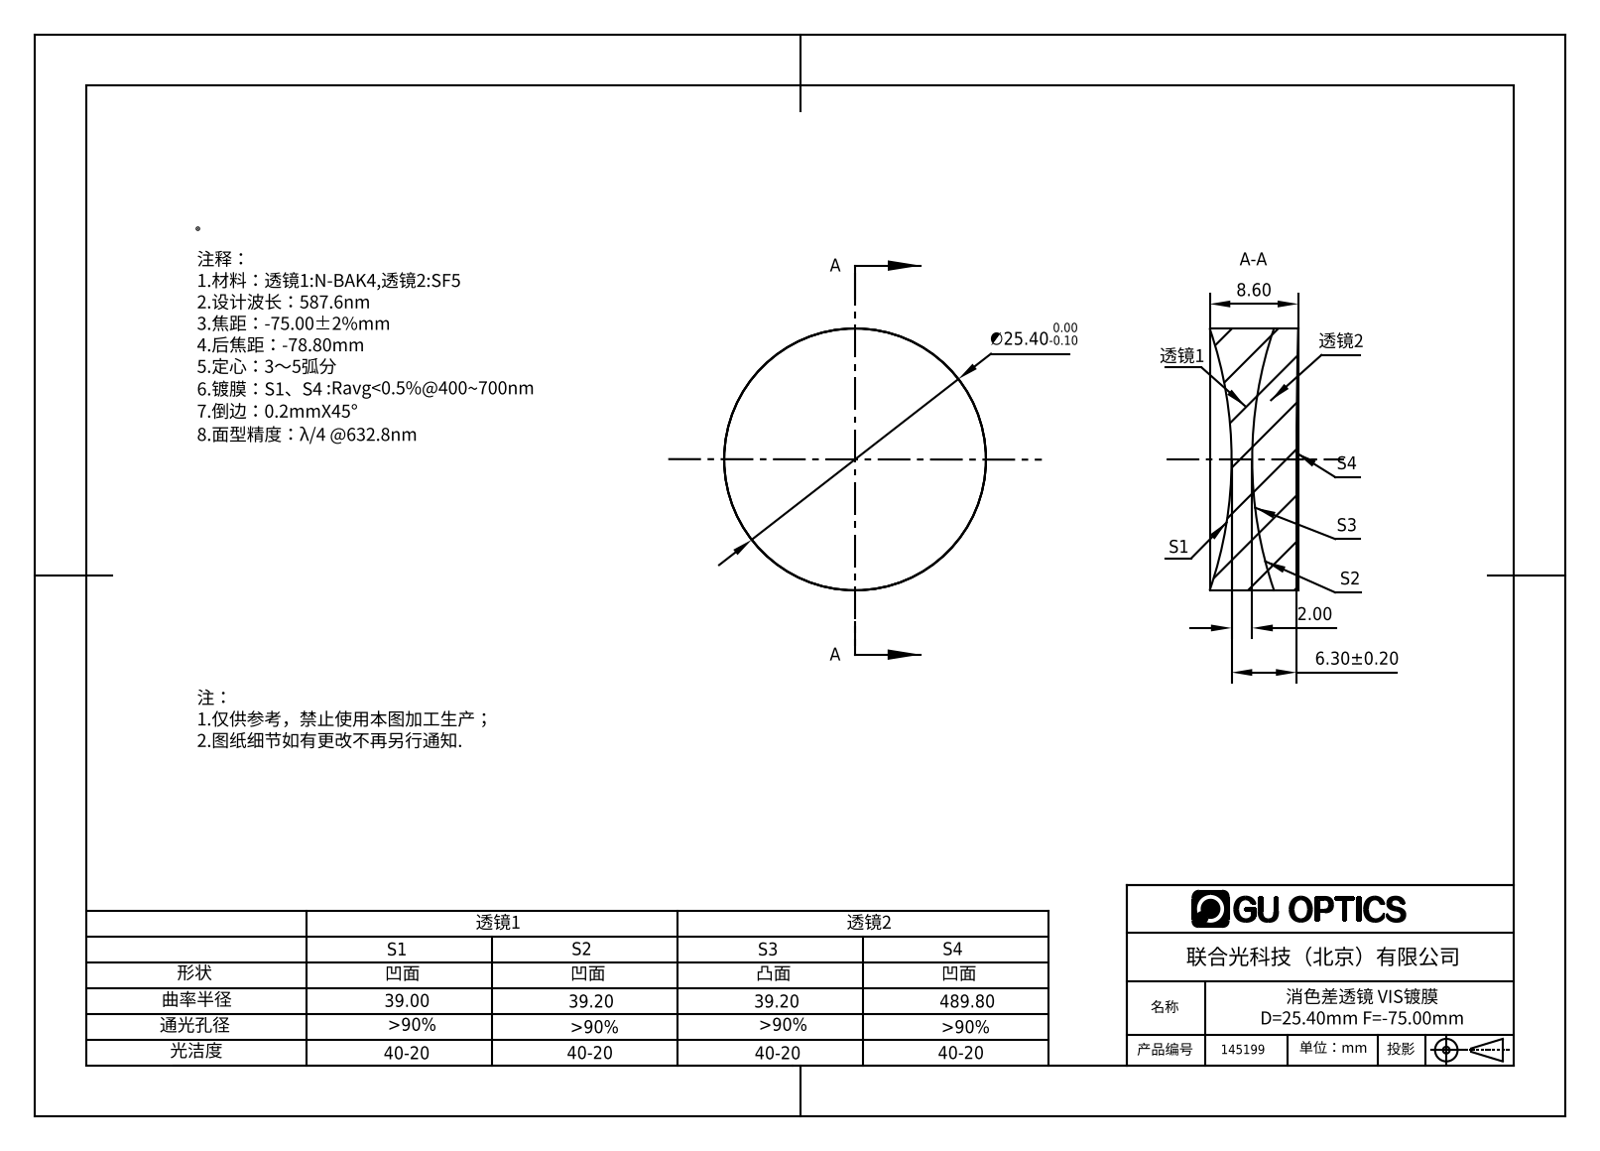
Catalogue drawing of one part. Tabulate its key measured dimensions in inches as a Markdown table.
| quantity | value |
| --- | --- |
| part name | 145199 |
| STEP written by | SolidWorks 2016 (AUTOMOTIVE_DESIGN) |
| units | inches |
| bodies | 2 solids, 12 faces (0 planar, 4 cylindrical, 8 other) |
| overall size | 1 × 1 × 0.338 |
| volume | 0.23 in³ |
| surface area | 4.27 in² |
| round bosses / shafts (diameter × count) | 1 × 1 |
